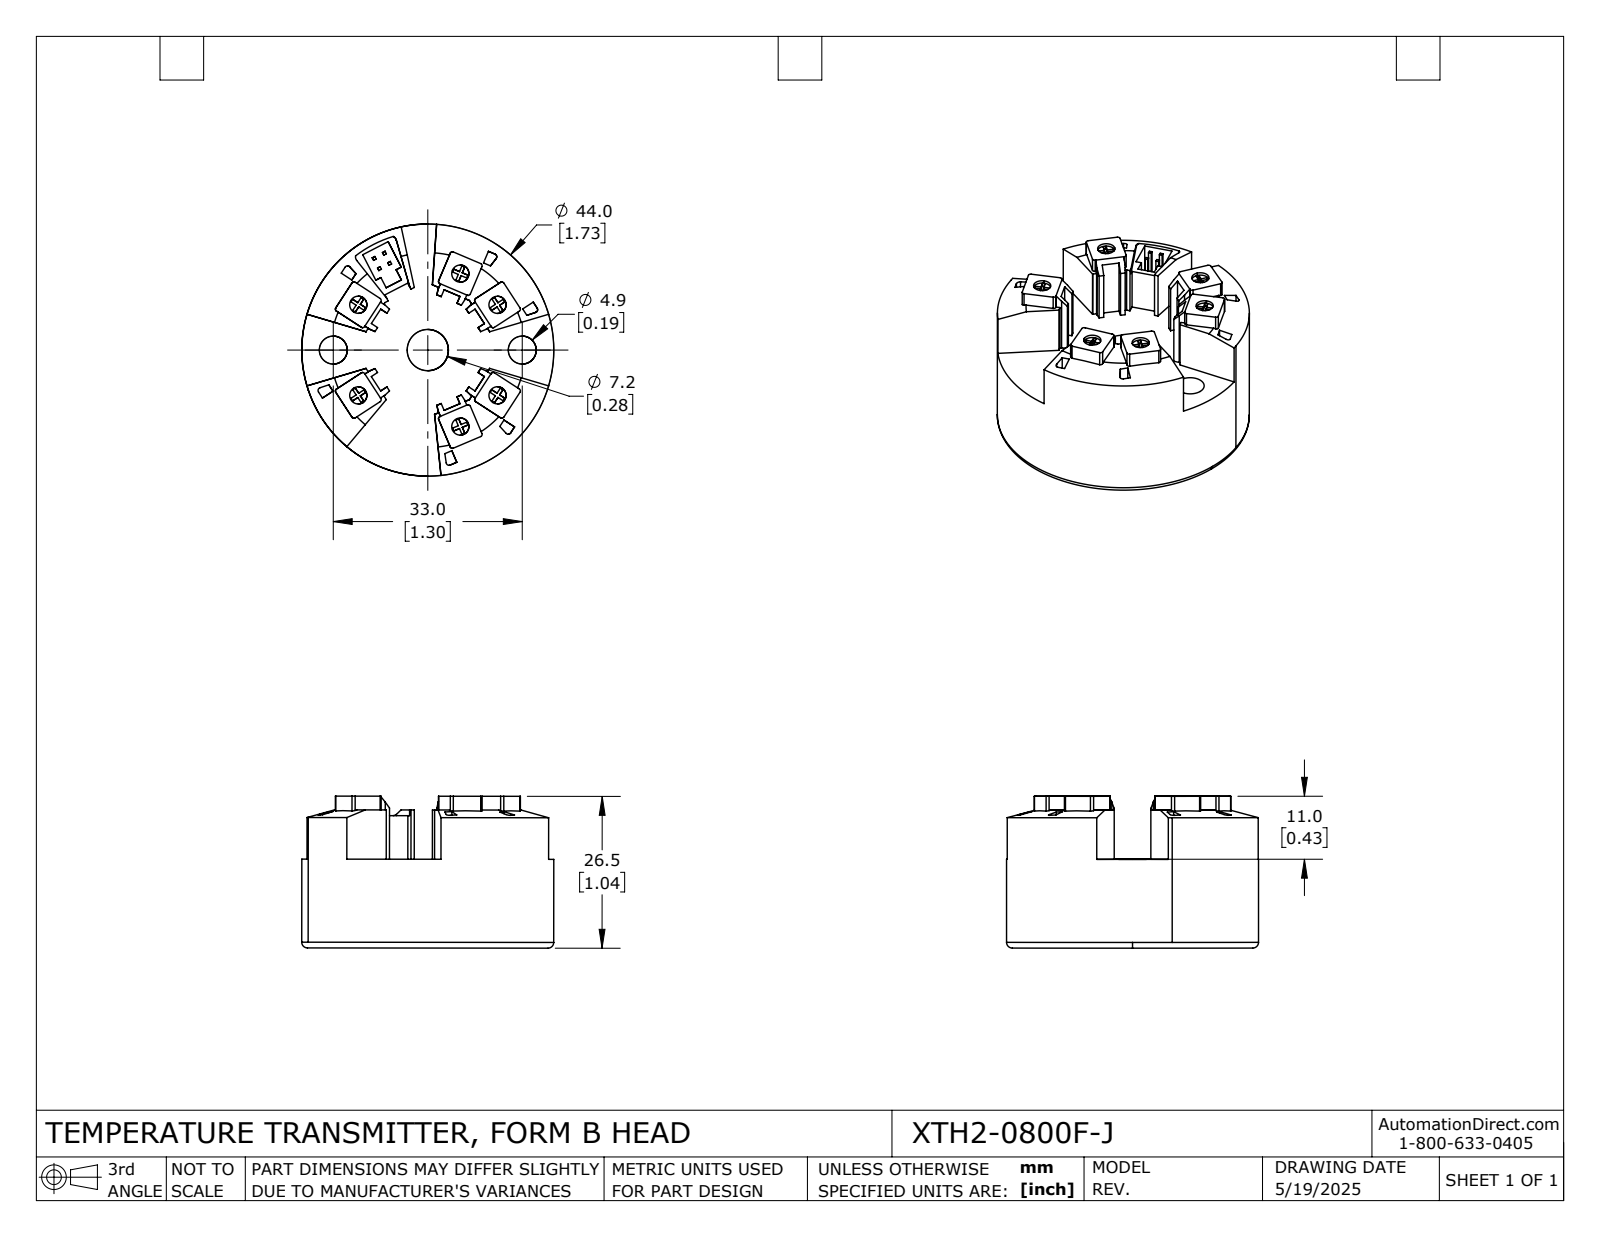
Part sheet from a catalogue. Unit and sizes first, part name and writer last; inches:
Units: inches
Overall size (bounding box): 1.733 × 1.732 × 1.045
Round holes (diameter × count): ⌀0.118 ×6, ⌀0.193 ×2, ⌀0.283 ×1
Round bosses / shafts (diameter × count): ⌀1.732 ×1
Partial cylindrical surfaces — rounded edges, fillets, slot ends (radius × count): R0.016 ×24, R0.02 ×6, R0.039 ×2
Main face-to-face distances: 0.61, 1.043, 0.433, 0.059, 0.177, 0.039, 0.02, 0.118, 0.949, 0.339
Hole centre spacings: 0.571, 0.333, 0.355, 0.356, 0.65, 0.677, 0.733, 0.875
Volume: 1.748 in³ · Surface area: 13.46 in²
Bodies: 1 solid, 341 faces (281 planar, 52 cylindrical, 8 other)
Part name (STEP PRODUCT): XTDH2-0800F-J
STEP written by: SolidWorks 2024 (AUTOMOTIVE_DESIGN)
